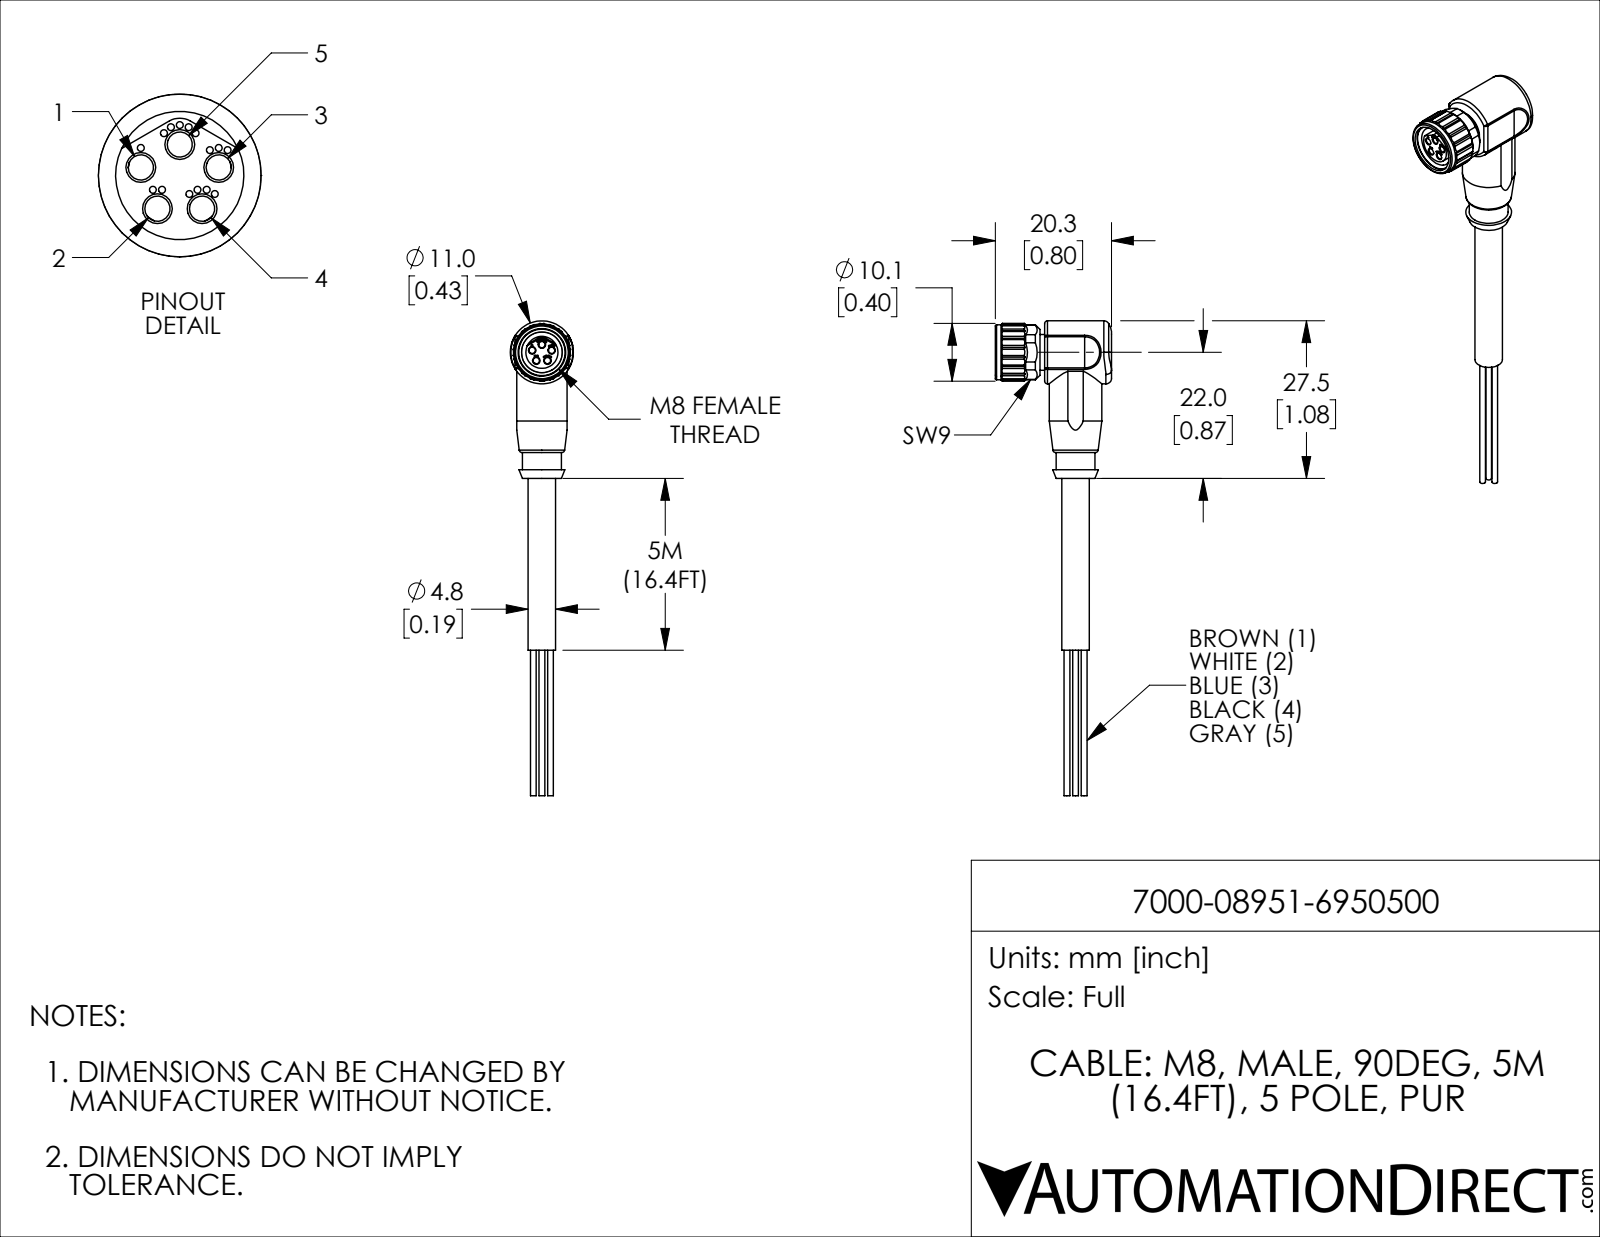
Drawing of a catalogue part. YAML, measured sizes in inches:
part_name: "7000-08951-6950500"
step_written_by: "SolidWorks 2019 (CONFIG_CONTROL_DESIGN)"
units: inches
bodies: {solids: 1, faces: 341, planar: 135, cylindrical: 152, other: 54}
overall_size: [3.264, 0.799, 0.433]
volume: 0.189
surface_area: 3.917
round_holes:
  - {diameter: 0.012, count: 15}
  - {diameter: 0.043, count: 5}
  - {diameter: 0.25, count: 1}
  - {diameter: 0.28, count: 1}
  - {diameter: 0.327, count: 1}
round_bosses_or_shafts:
  - {diameter: 0.039, count: 5}
  - {diameter: 0.433, count: 1}
  - {diameter: 0.378, count: 1}
  - {diameter: 0.362, count: 1}
  - {diameter: 0.268, count: 1}
  - {diameter: 0.246, count: 1}
  - {diameter: 0.22, count: 1}
  - {diameter: 0.189, count: 1}
partial_cylinders:
  - {radius: 0.079, count: 18}
  - {radius: 0.02, count: 8}
  - {radius: 0.03, count: 6}
  - {radius: 0.033, count: 4}
  - {radius: 0.008, count: 2}
  - {radius: 0.138, count: 2}
  - {radius: 0.197, count: 2}
  - {radius: 0.022, count: 1}
face_to_face_distances: [0.358, 0.461, 0.37, 0.346, 0.357, 0.031, 0.492, 0.354, 0.77, 0.309]
hole_center_spacings: [0.033, 0.016, 0.078, 0.031, 0.044, 0.069, 0.076, 0.099]
